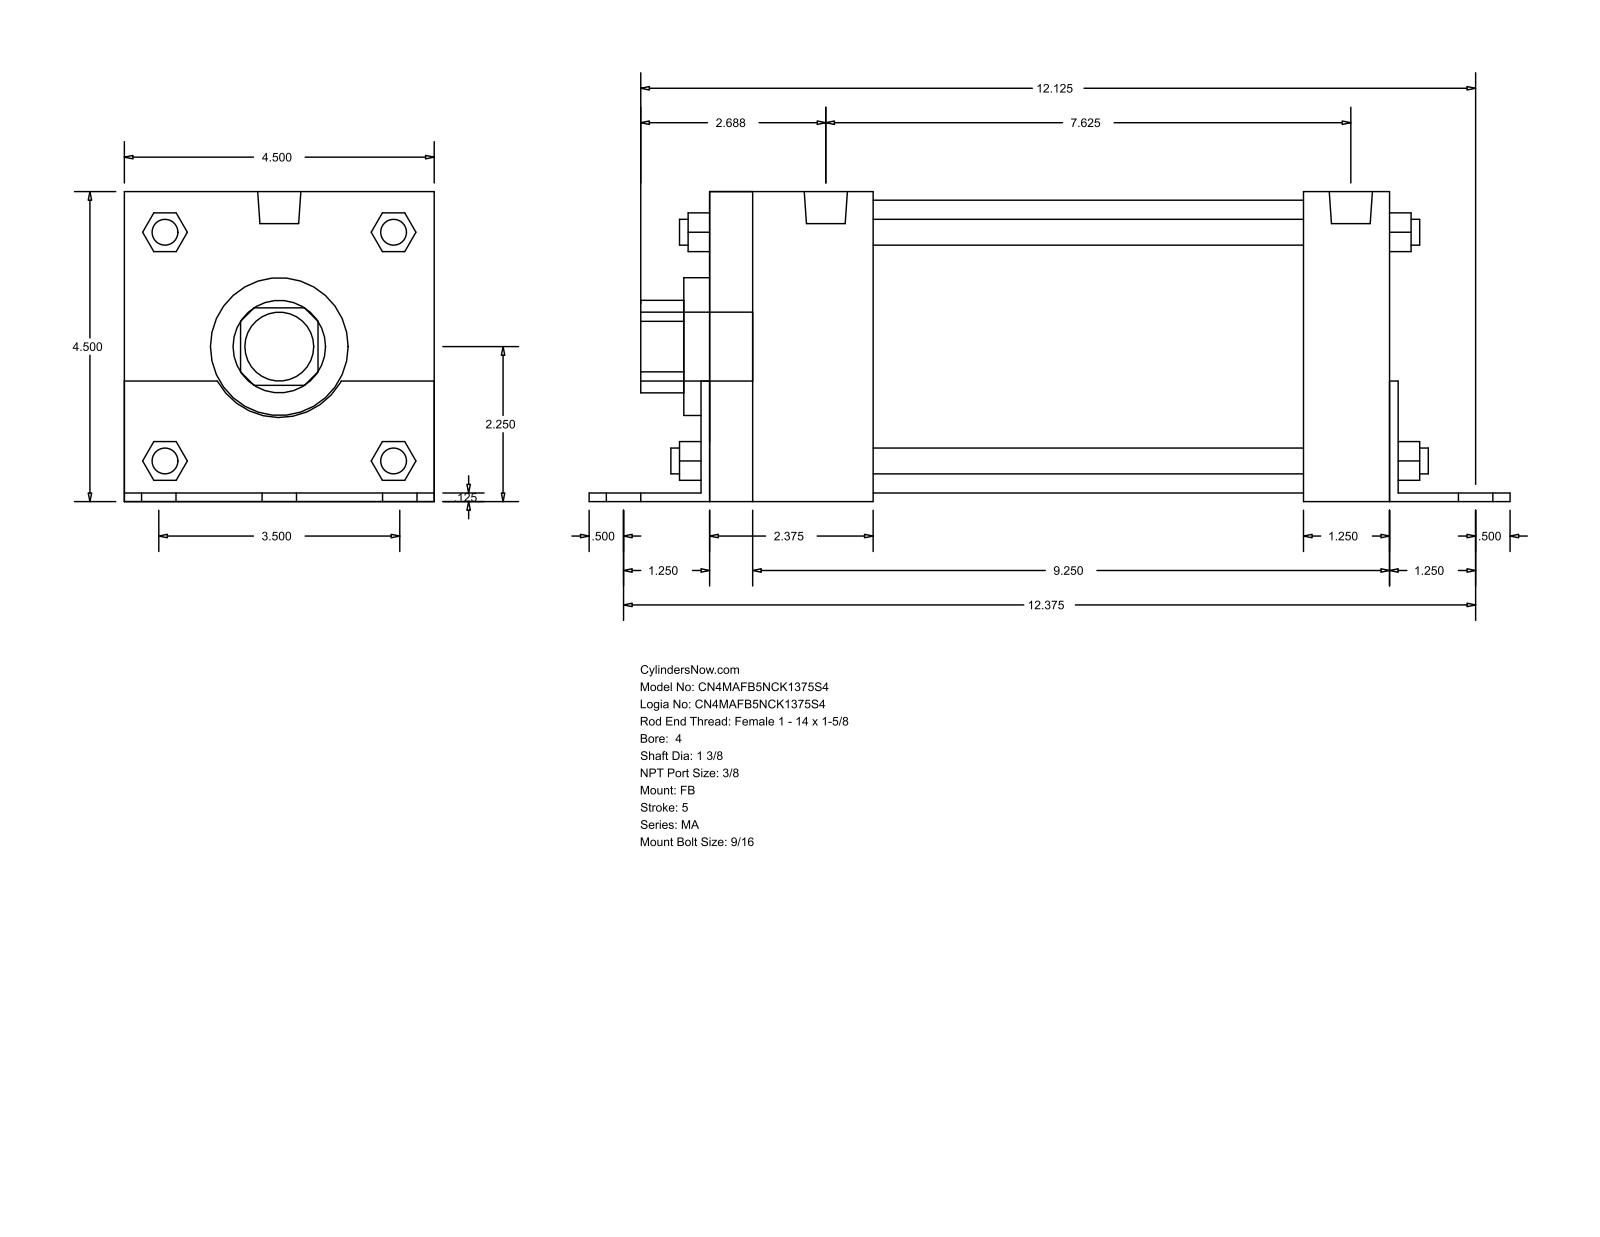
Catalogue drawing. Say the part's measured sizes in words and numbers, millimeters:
The part is named "MA_FB__0400_1.375". Its 3-D file was written by "GSSL Pune (CONFIG_CONTROL_DESIGN)". It is 0 solids with 140 faces: 105 planar, 35 cylindrical and 0 other. Overall it measures 339.73 by 114.35 by 114.3 millimeters. Round holes: 1 of diameter 34.92, 1 of diameter 50.8, 1 of diameter 107.95. Round bosses or shafts: 6 of diameter 14.29, 4 of diameter 11.11, 4 of diameter 9.53, 2 of diameter 15.93, 1 of diameter 25.4. Partial cylindrical surfaces (rounded edges, fillets, slot ends): 1 of radius 17.06, 1 of radius 26.16. The main face-to-face distances are 114.3, 3.17, 114.35, 3.12, 111.18, 254, 250.83, 34.93, 60.32, 257.17.
